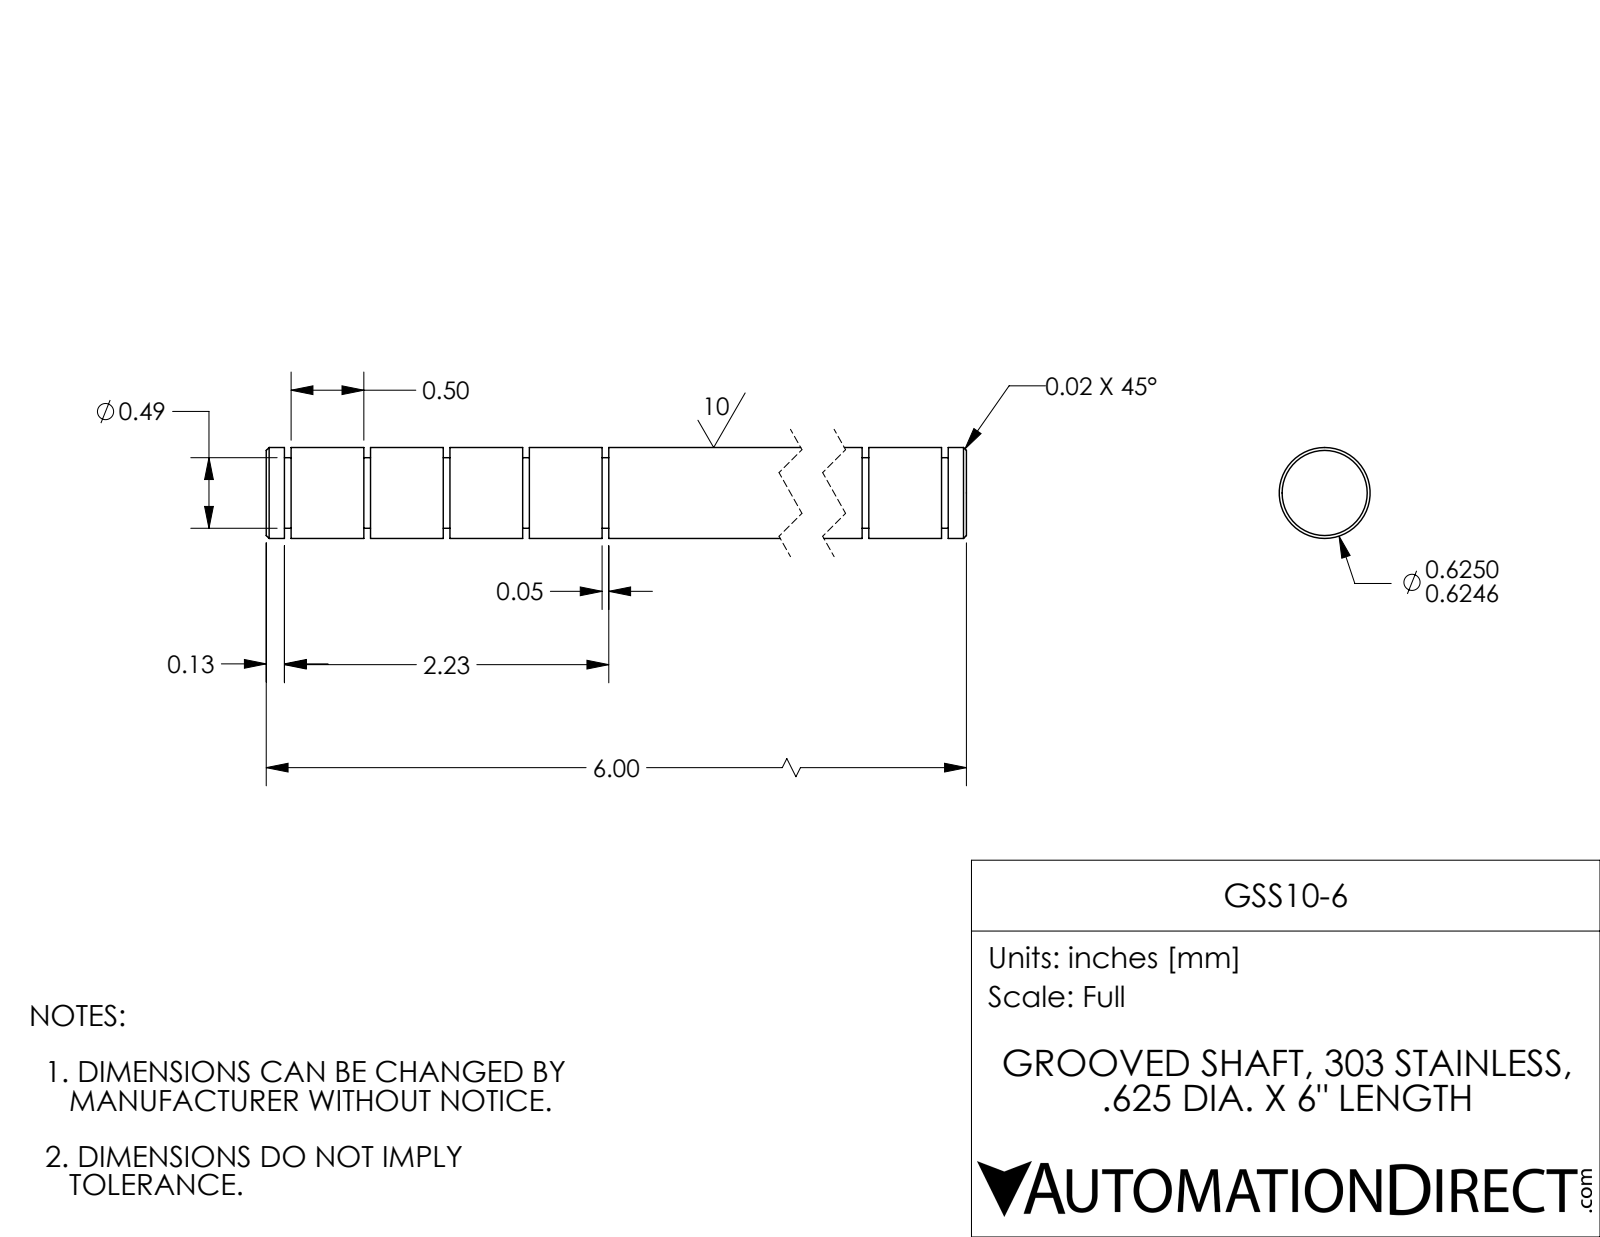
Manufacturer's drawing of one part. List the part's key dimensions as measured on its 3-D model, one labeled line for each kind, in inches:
Part name (STEP PRODUCT): GSS10-6
STEP written by: SolidWorks 2017 (AUTOMOTIVE_DESIGN)
Units: inches
Bodies: 1 solid, 50 faces (16 planar, 30 cylindrical, 4 other)
Overall size (bounding box): 6 × 0.625 × 0.625
Volume: 1.801 in³ · Surface area: 13.91 in²
Round bosses / shafts (diameter × count): ⌀0.625 ×1, ⌀0.485 ×1
Main face-to-face distances: 0.546, 0.046, 1.092, 0.5, 0.592, 1.638, 1.138, 5.158, 1.046, 4.612
